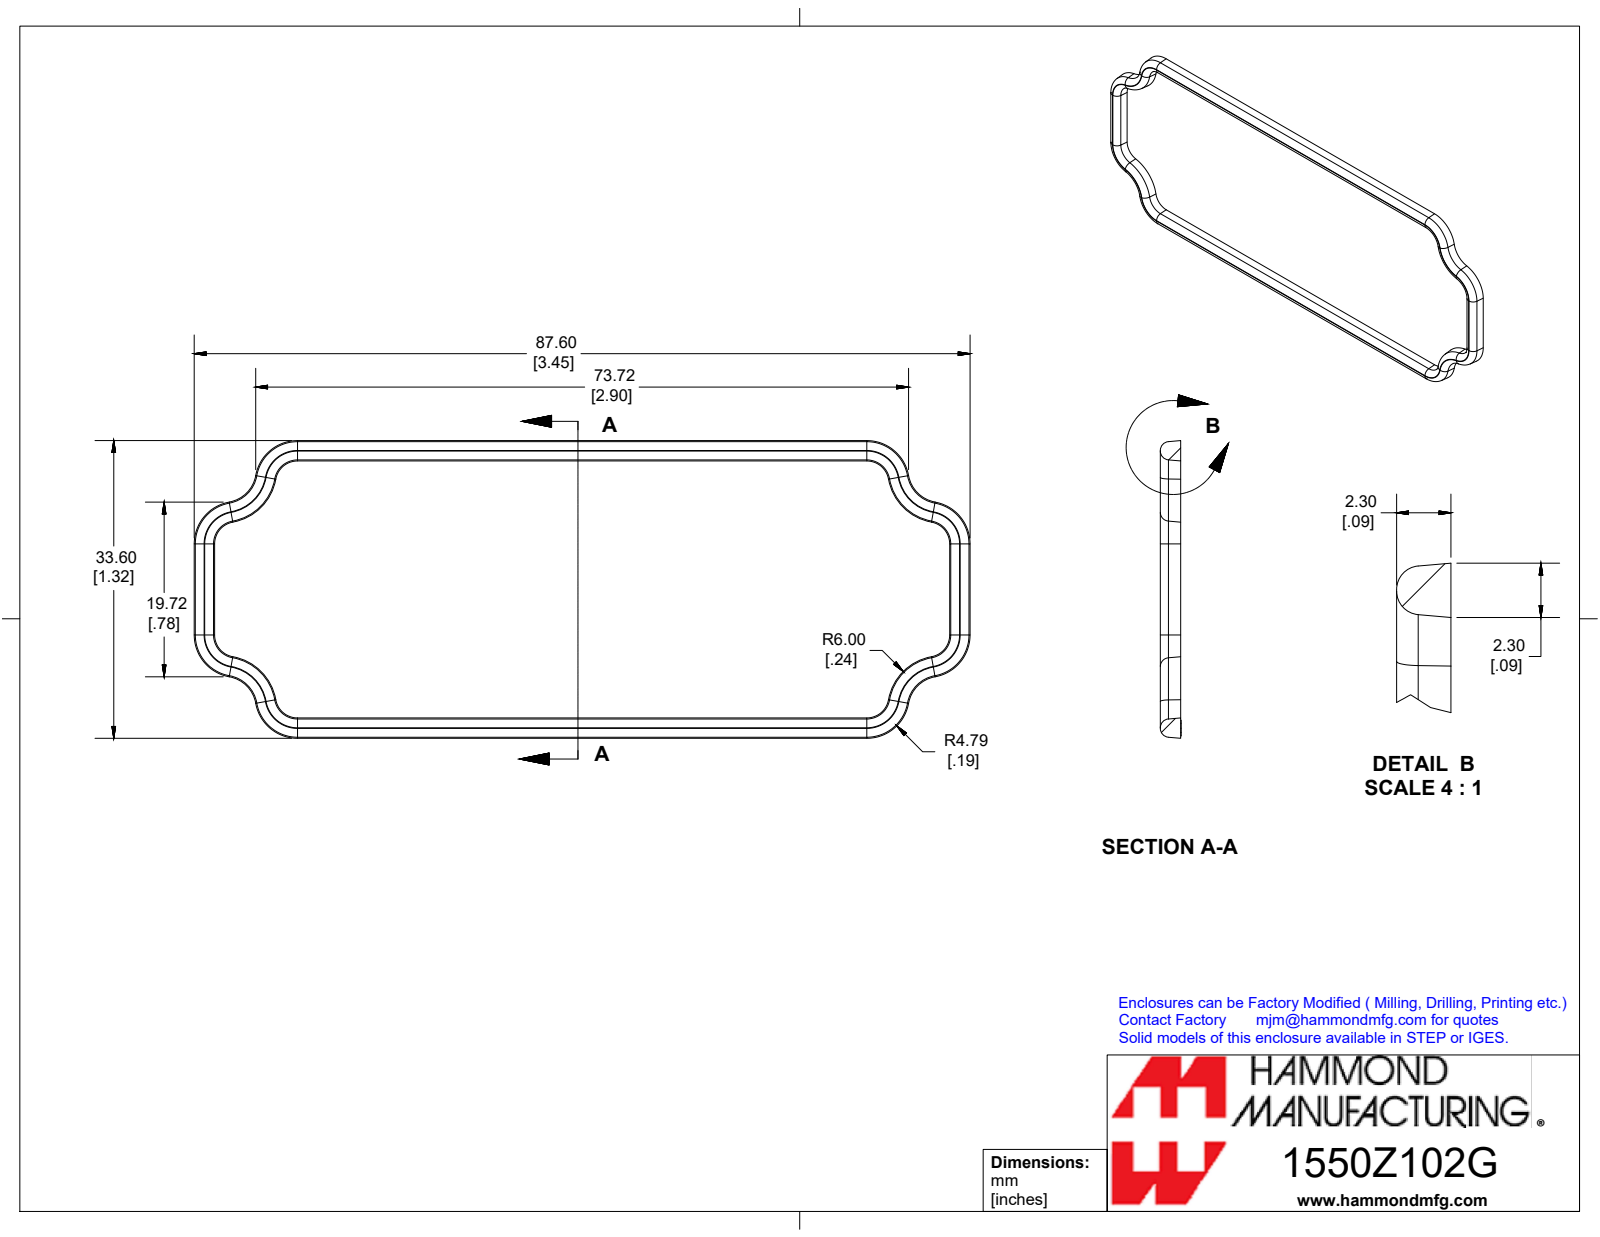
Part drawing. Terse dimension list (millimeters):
name: 1550Z102GASKET
written by: SolidWorks 2019 (CONFIG_CONTROL_DESIGN)
unit: mm
bodies: 1 solid, 123 faces (25 planar, 8 cylindrical, 90 other)
size: 87.6 × 33.6 × 2.4
volume: 950 mm³; area: 1 734 mm²
rounds: 8× R1
face distances: 31.2, 84.9, 2.3, 2.4, 1.4, 0.3, 1.7, 1.2
